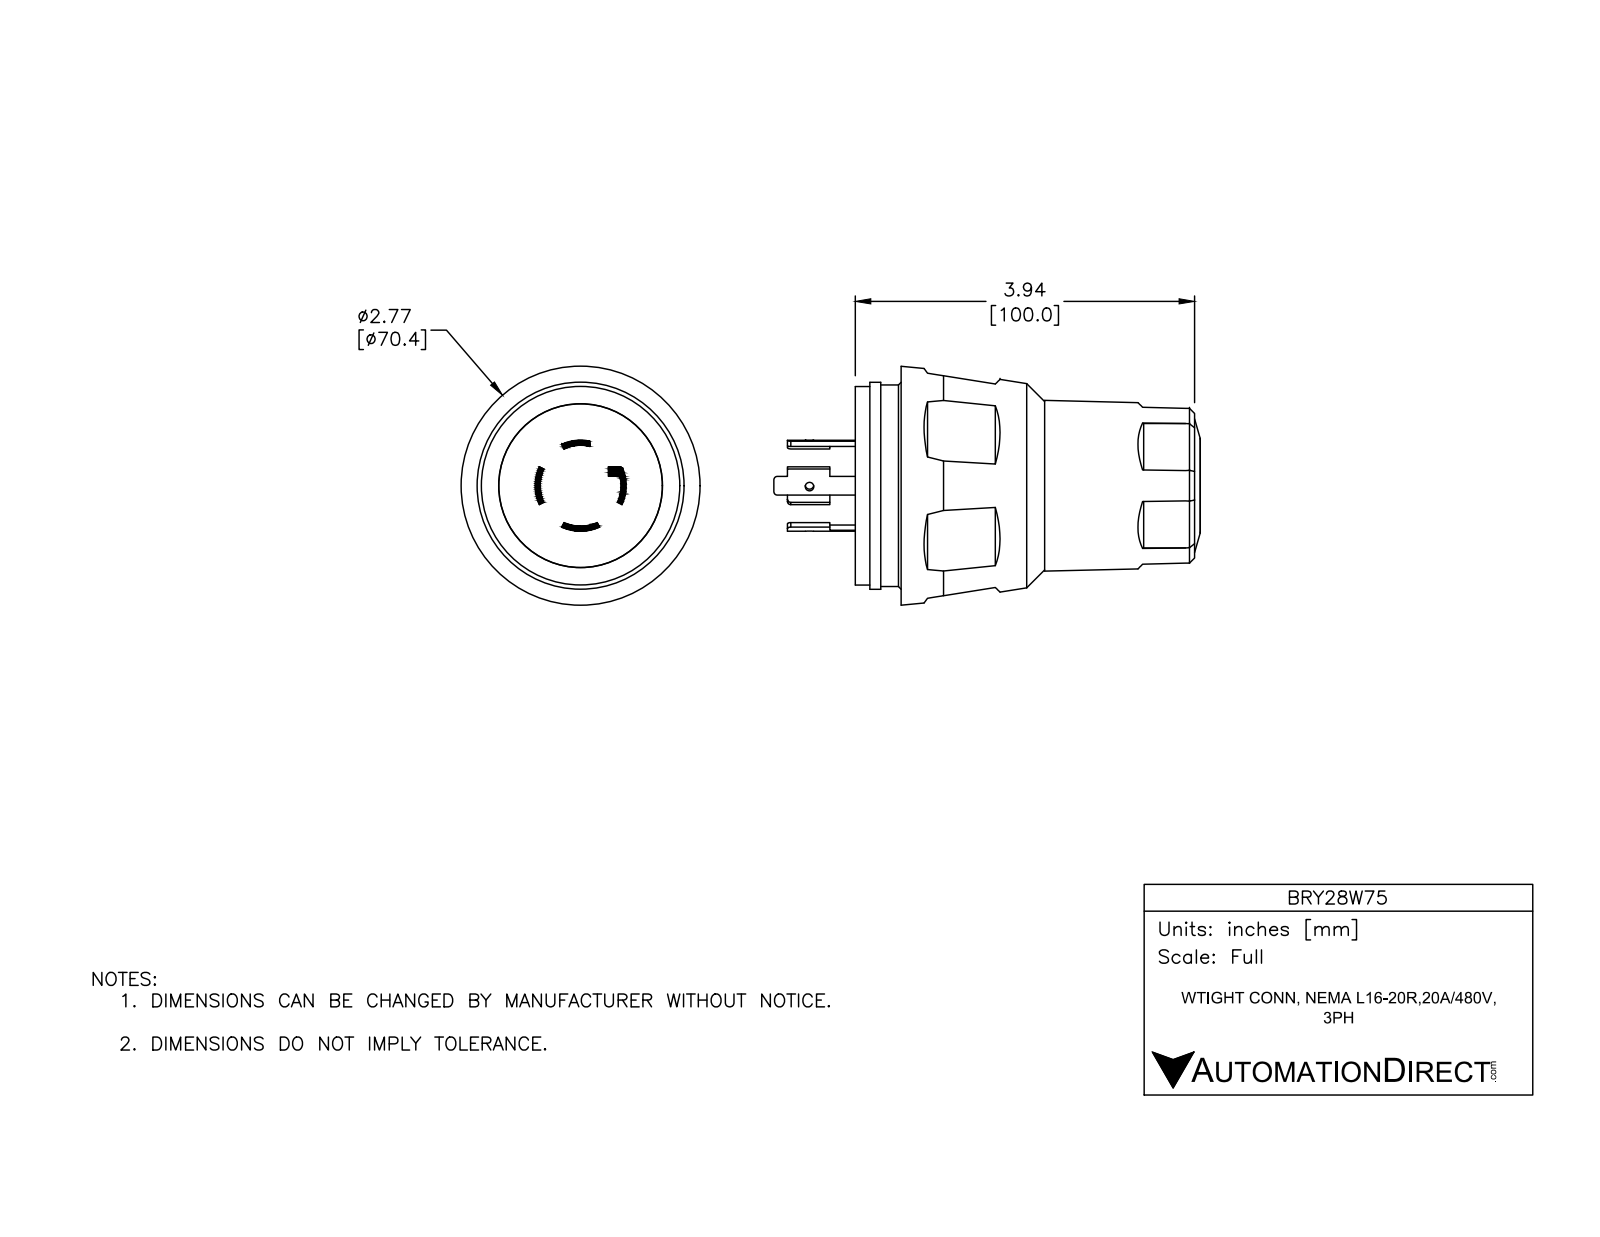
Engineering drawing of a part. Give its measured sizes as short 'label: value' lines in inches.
name: BRY28W75
written by: SolidWorks 2016 (AUTOMOTIVE_DESIGN)
unit: in
bodies: 8 solids, 201 faces (116 planar, 62 cylindrical, 23 other)
size: 4.948 × 2.772 × 2.772
volume: 14.59 in³; area: 69.67 in²
holes: 4× ⌀0.098, 1× ⌀1, 1× ⌀1.902
bosses: 1× ⌀2.402, 1× ⌀2.339, 1× ⌀2.303, 1× ⌀1.898, 1× ⌀1.551
rounds: 10× R0.039, 1× R0.449, 1× R0.469, 1× R0.528, 1× R0.547
face distances: 0.276, 3.031, 3.307, 2.776, 0.256, 0.531, 0.551, 3.327, 3.583, 3.858
hole spacings: 0.02
